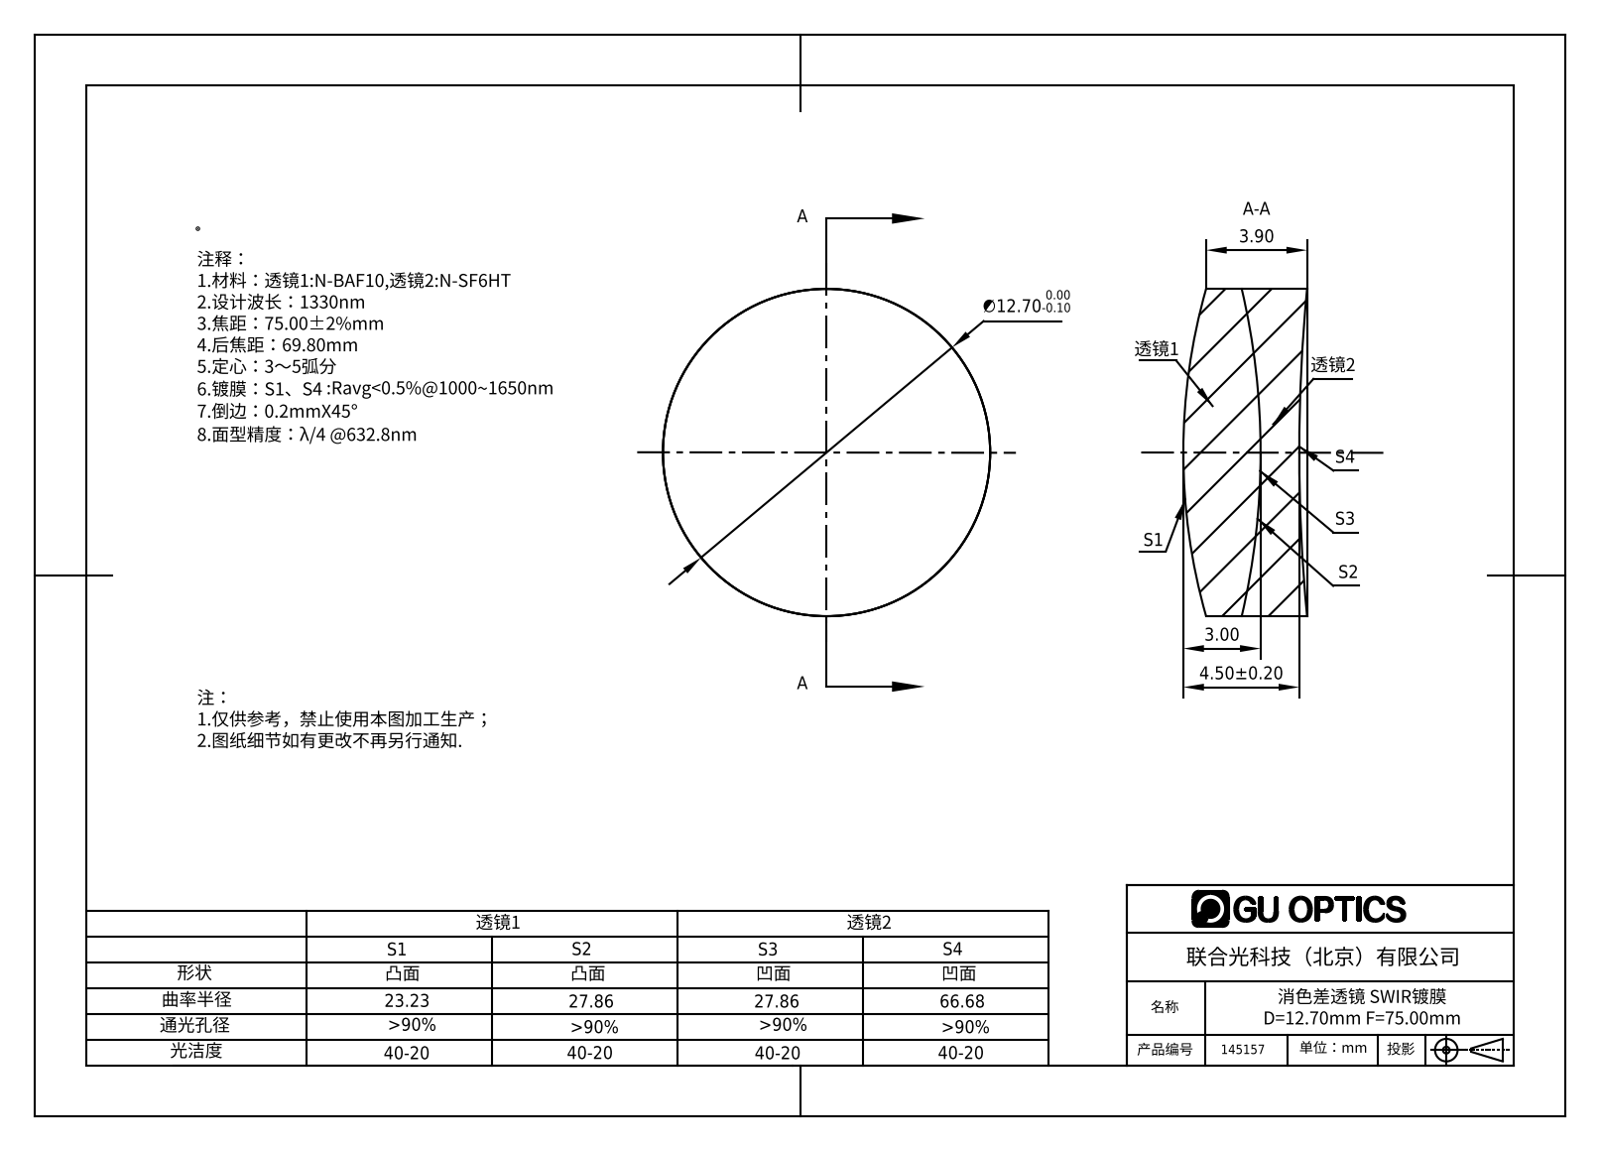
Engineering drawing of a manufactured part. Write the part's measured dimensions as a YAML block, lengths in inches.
part_name: "145157"
step_written_by: "SolidWorks 2016 (AUTOMOTIVE_DESIGN)"
units: inches
bodies: {solids: 2, faces: 12, planar: 0, cylindrical: 4, other: 8}
overall_size: [0.5, 0.5, 0.189]
volume: 0.033
surface_area: 1.04
round_bosses_or_shafts:
  - {diameter: 0.5, count: 1}
